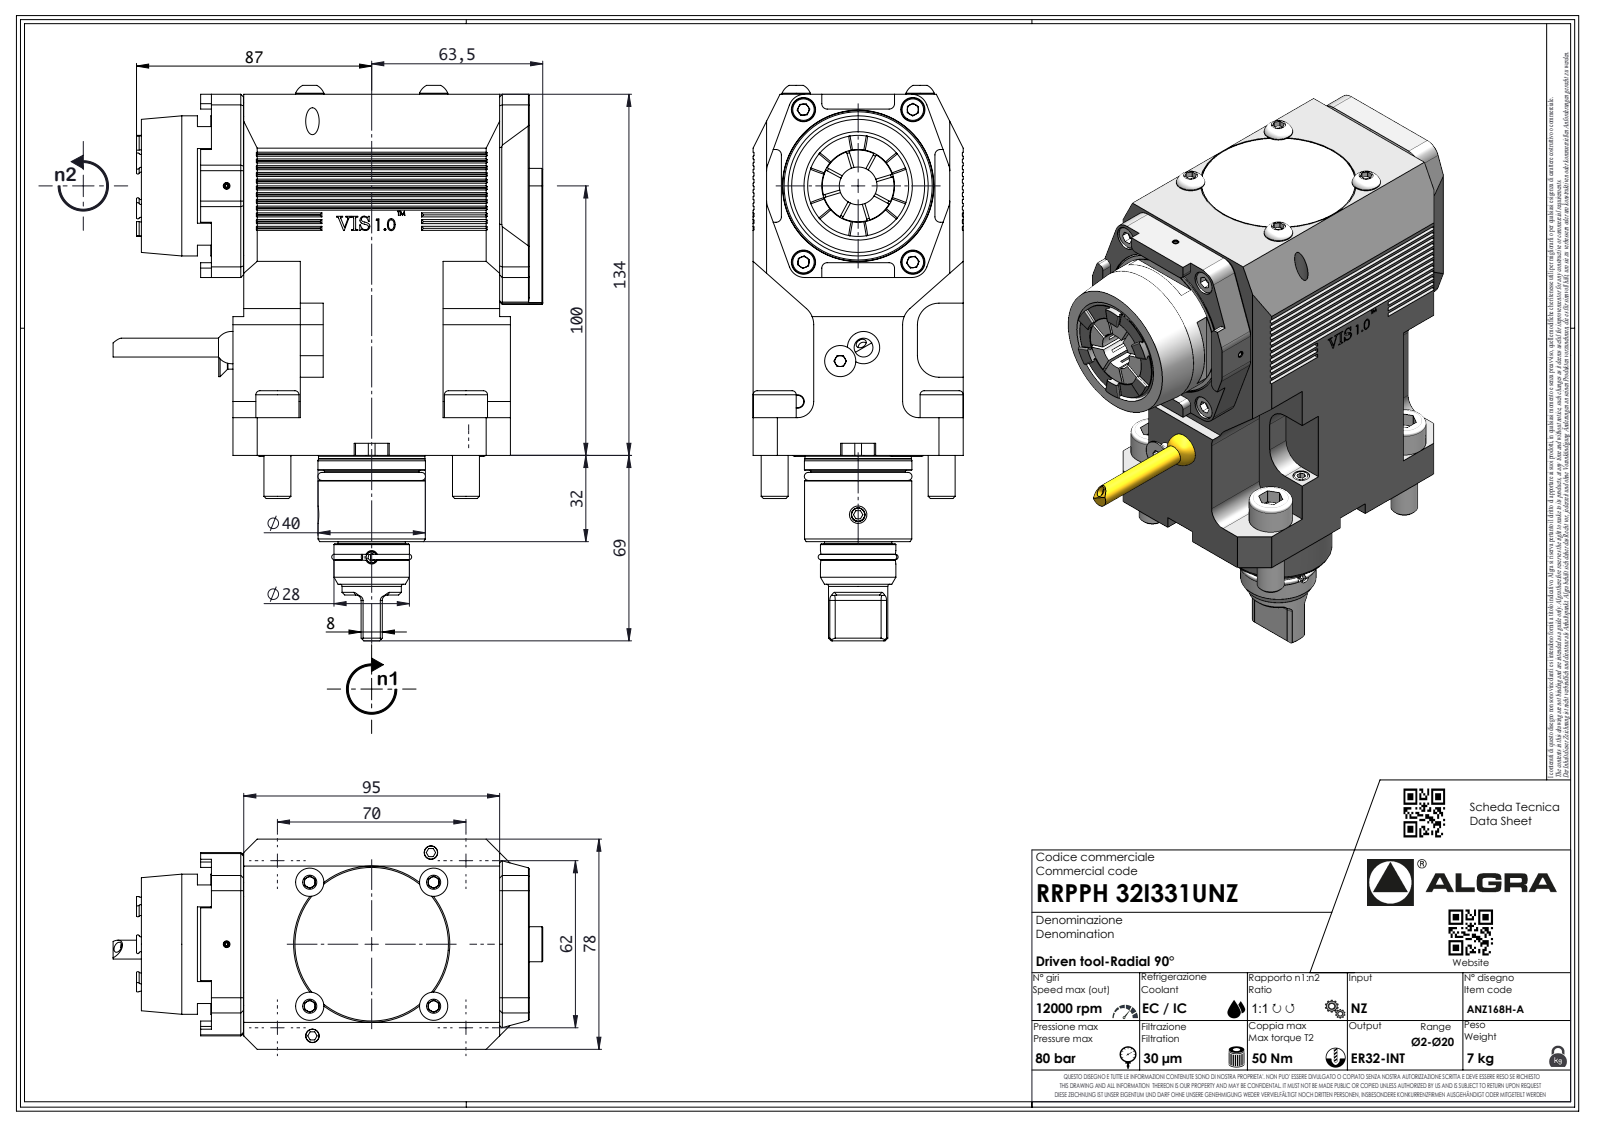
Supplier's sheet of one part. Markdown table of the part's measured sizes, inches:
| quantity | value |
| --- | --- |
| part name | RRPPH32I331UNZ |
| STEP written by | SolidWorks 2023 (AUTOMOTIVE_DESIGN) |
| units | inches |
| bodies | 1 solid, 872 faces (587 planar, 120 cylindrical, 165 other) |
| overall size | 7.984 × 6.28 × 3.071 |
| volume | 67.25 in³ |
| surface area | 146.1 in² |
| round holes (diameter × count) | 0.083 × 1, 0.157 × 1, 0.319 × 1 |
| round bosses / shafts (diameter × count) | 0.63 × 4, 0.394 × 4, 2.047 × 1, 1.571 × 1, 1.567 × 1, 1.555 × 1, 1.382 × 1, 1.378 × 1 |
| partial cylindrical surfaces (radius × count) | 0.197 × 16, 0.079 × 15, 0.236 × 10, 0.013 × 7, 0.02 × 7, 0.146 × 7, 0.315 × 6, 0.02 × 2 |
| main face-to-face distances | 3.071, 5.276, 0.157, 0.472, 0.984, 3.898, 4.173, 0.886, 2.913, 0.827 |
